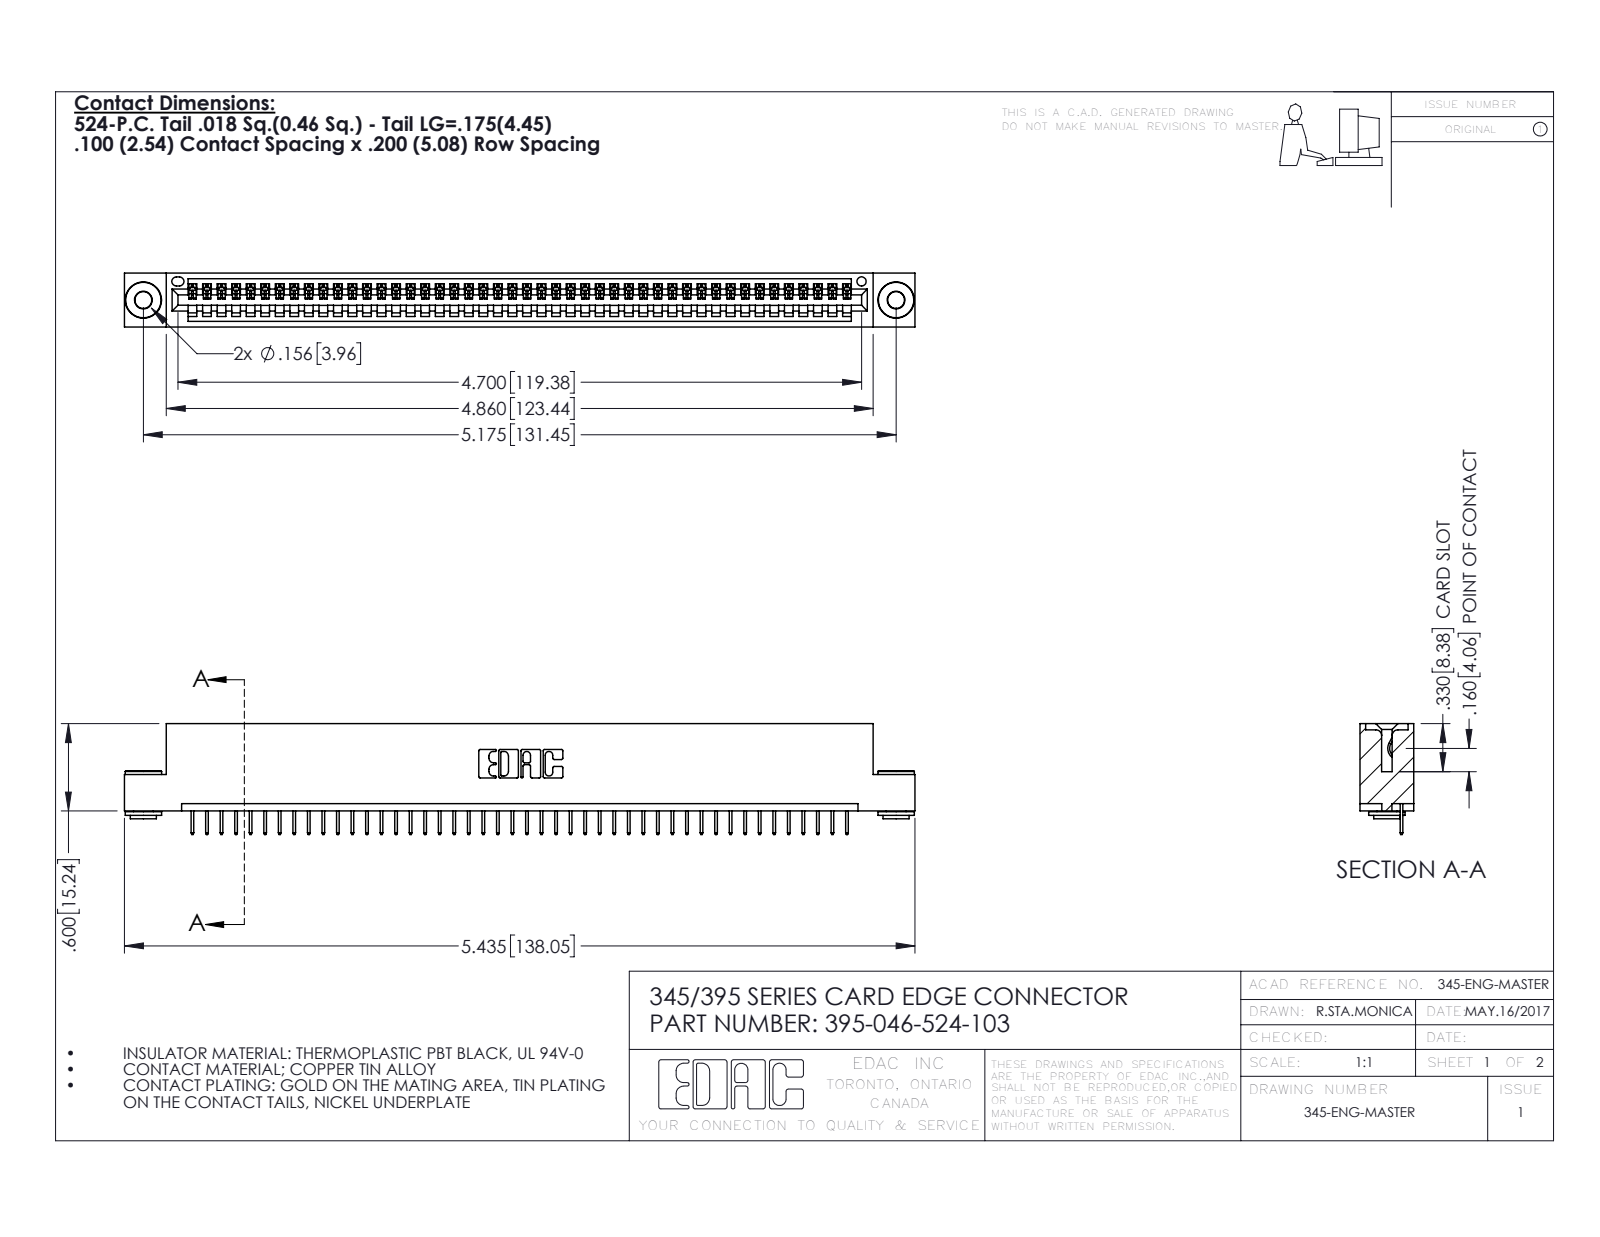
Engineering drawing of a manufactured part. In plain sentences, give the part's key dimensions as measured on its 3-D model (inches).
The part is named "395-046-524-103; 345 Part_Flush Mounting Lugs - 0.156 Dia-TH; 345-250-002_345-250-002-102; 345-292-001_345-293-124". Its 3-D file was written by "SolidWorks 2016 (CONFIG_CONTROL_DESIGN)". It is 49 solids with 3016 faces: 2206 planar, 802 cylindrical and 8 other. Overall it measures 5.435 by 0.762 by 0.37 inches. Its volume is 0.792 cubic inches and its surface area 26.26 square inches. Round holes: 2 of diameter 0.116, 2 of diameter 0.156, 1 of diameter 0.064. Round bosses or shafts: 2 of diameter 0.25, 2 of diameter 0.18, 2 of diameter 0.136. Partial cylindrical surfaces (rounded edges, fillets, slot ends): 92 of radius 0.006, 22 of radius 0.01, 6 of radius 0.007, 6 of radius 0.031, 3 of radius 0.026, 2 of radius 0.031, 2 of radius 0.04, 1 of radius 0.014. The main face-to-face distances are 0.072, 0.298, 0.37, 0.2, 0.025, 0.098, 0.272, 0.225, 0.072, 0.149. The hole center spacings are 0.27, 4.939, 5.175.
